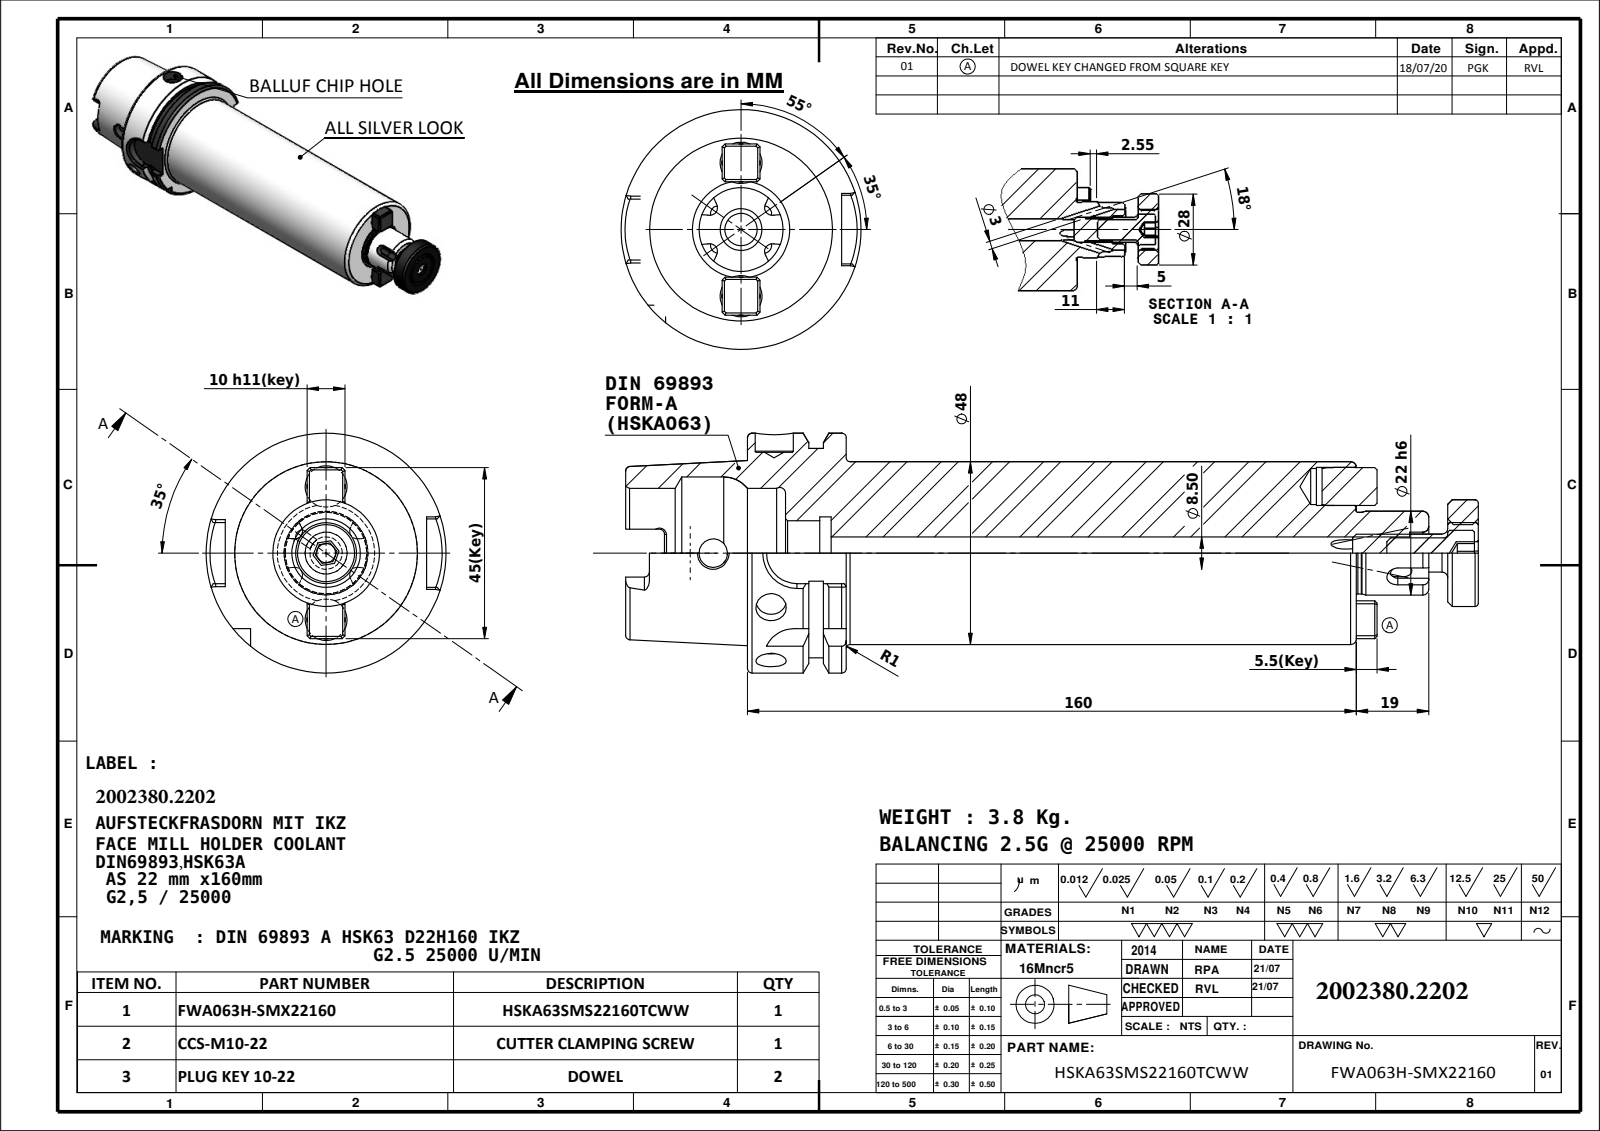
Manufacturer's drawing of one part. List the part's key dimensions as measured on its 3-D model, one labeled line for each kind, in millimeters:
Part name (STEP PRODUCT): CCS-M8-16-1.IGS; CCS-M10-22-2.IGS; CCS-M10-22-1 LONG.IGS; HSKA63SMS22160TCWW.IGS (+2 more)
STEP written by: SolidWorks 2018 (AUTOMOTIVE_DESIGN)
Units: millimetres
Bodies: 6 solids, 378 faces (0 planar, 0 cylindrical, 378 other)
Overall size (bounding box): 223.95 × 63 × 63
Volume: 329 307 mm³ · Surface area: 54 687 mm²
